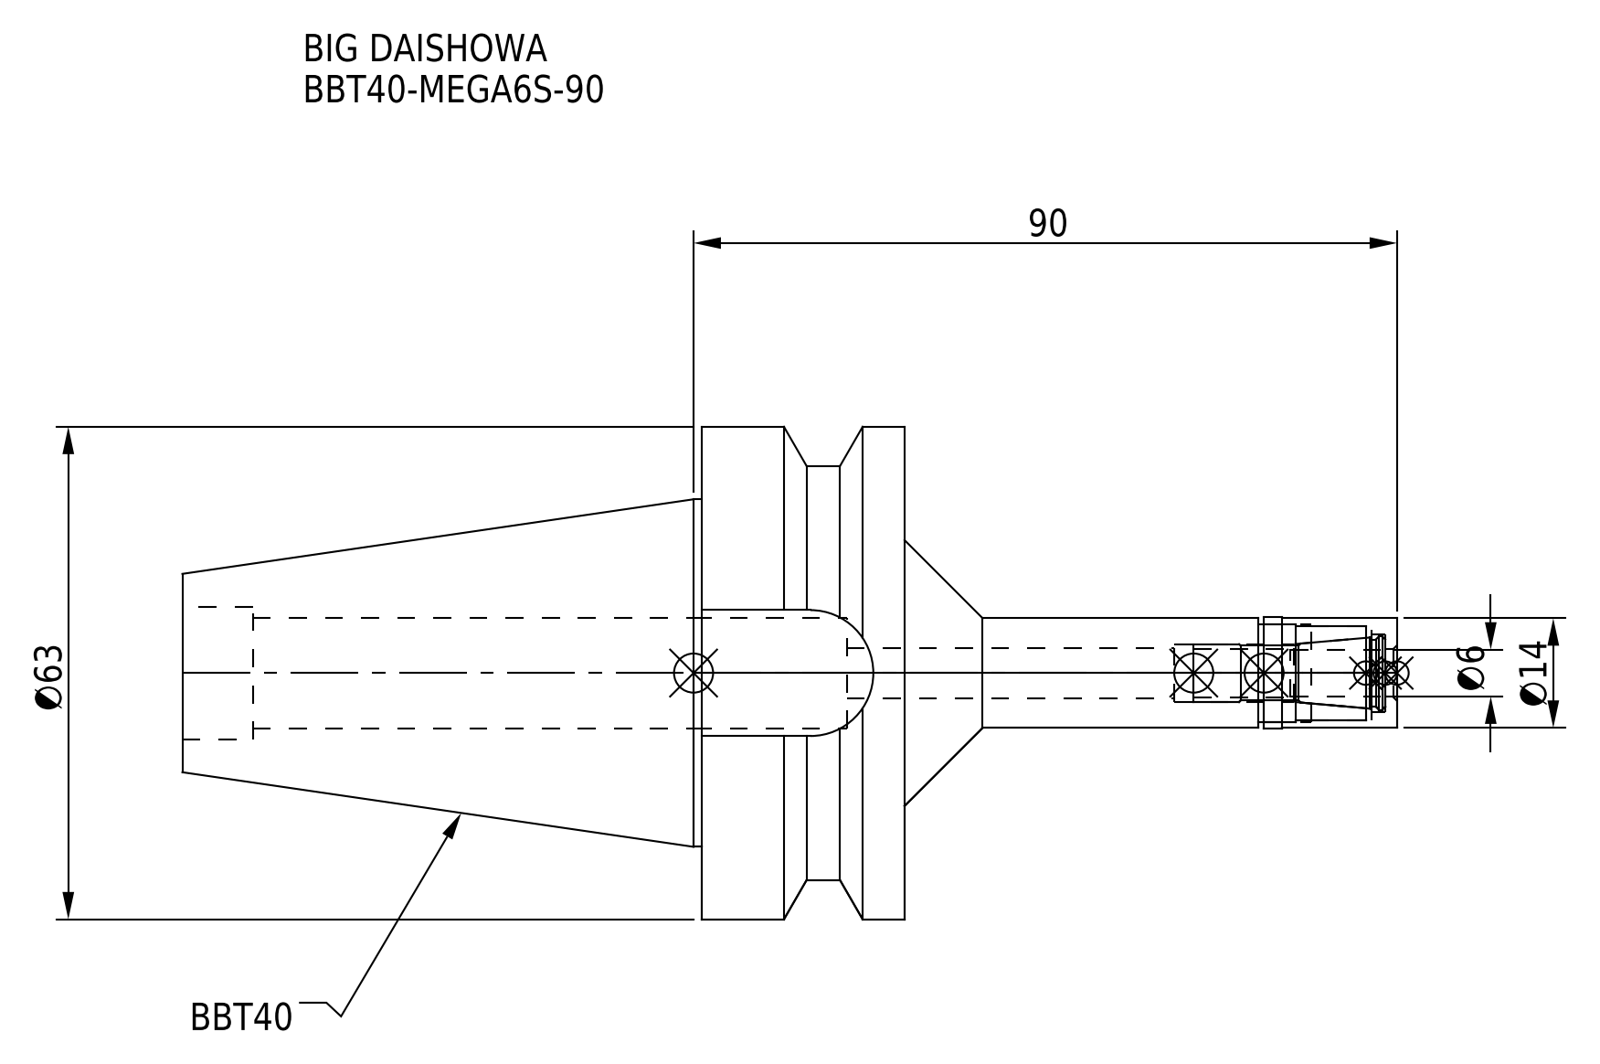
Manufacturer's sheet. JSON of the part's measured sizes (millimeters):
{"part_name": "MGN6S_1.stp; BBT40-MEGA6S-90; DXF_TEMP_ASSY_ASM_4_ASM.stp; BBT40MS06090-060_ASM.stp (+3 more)", "step_written_by": "SolidWorks 2019 (CONFIG_CONTROL_DESIGN)", "units": "millimeters", "bodies": {"solids": 2, "faces": 71, "planar": 21, "cylindrical": 38, "other": 12}, "overall_size": [155.4, 63, 63], "volume_mm3": 131660, "surface_area_mm2": 28041, "round_holes": [[6.1, 1], [6.4, 1], [7.4, 1], [10, 1], [12, 1], [12.5, 1], [14.2, 1], [17, 1]], "round_bosses_or_shafts": [[63, 1], [53, 1], [44.45, 1], [14.3, 1], [14, 1]], "partial_cylinders_radius": [[8.05, 1]], "face_to_face_distances": [26, 66.4, 45, 92.4, 16.1, 85, 7.4, 18.6, 63, 70.4]}
